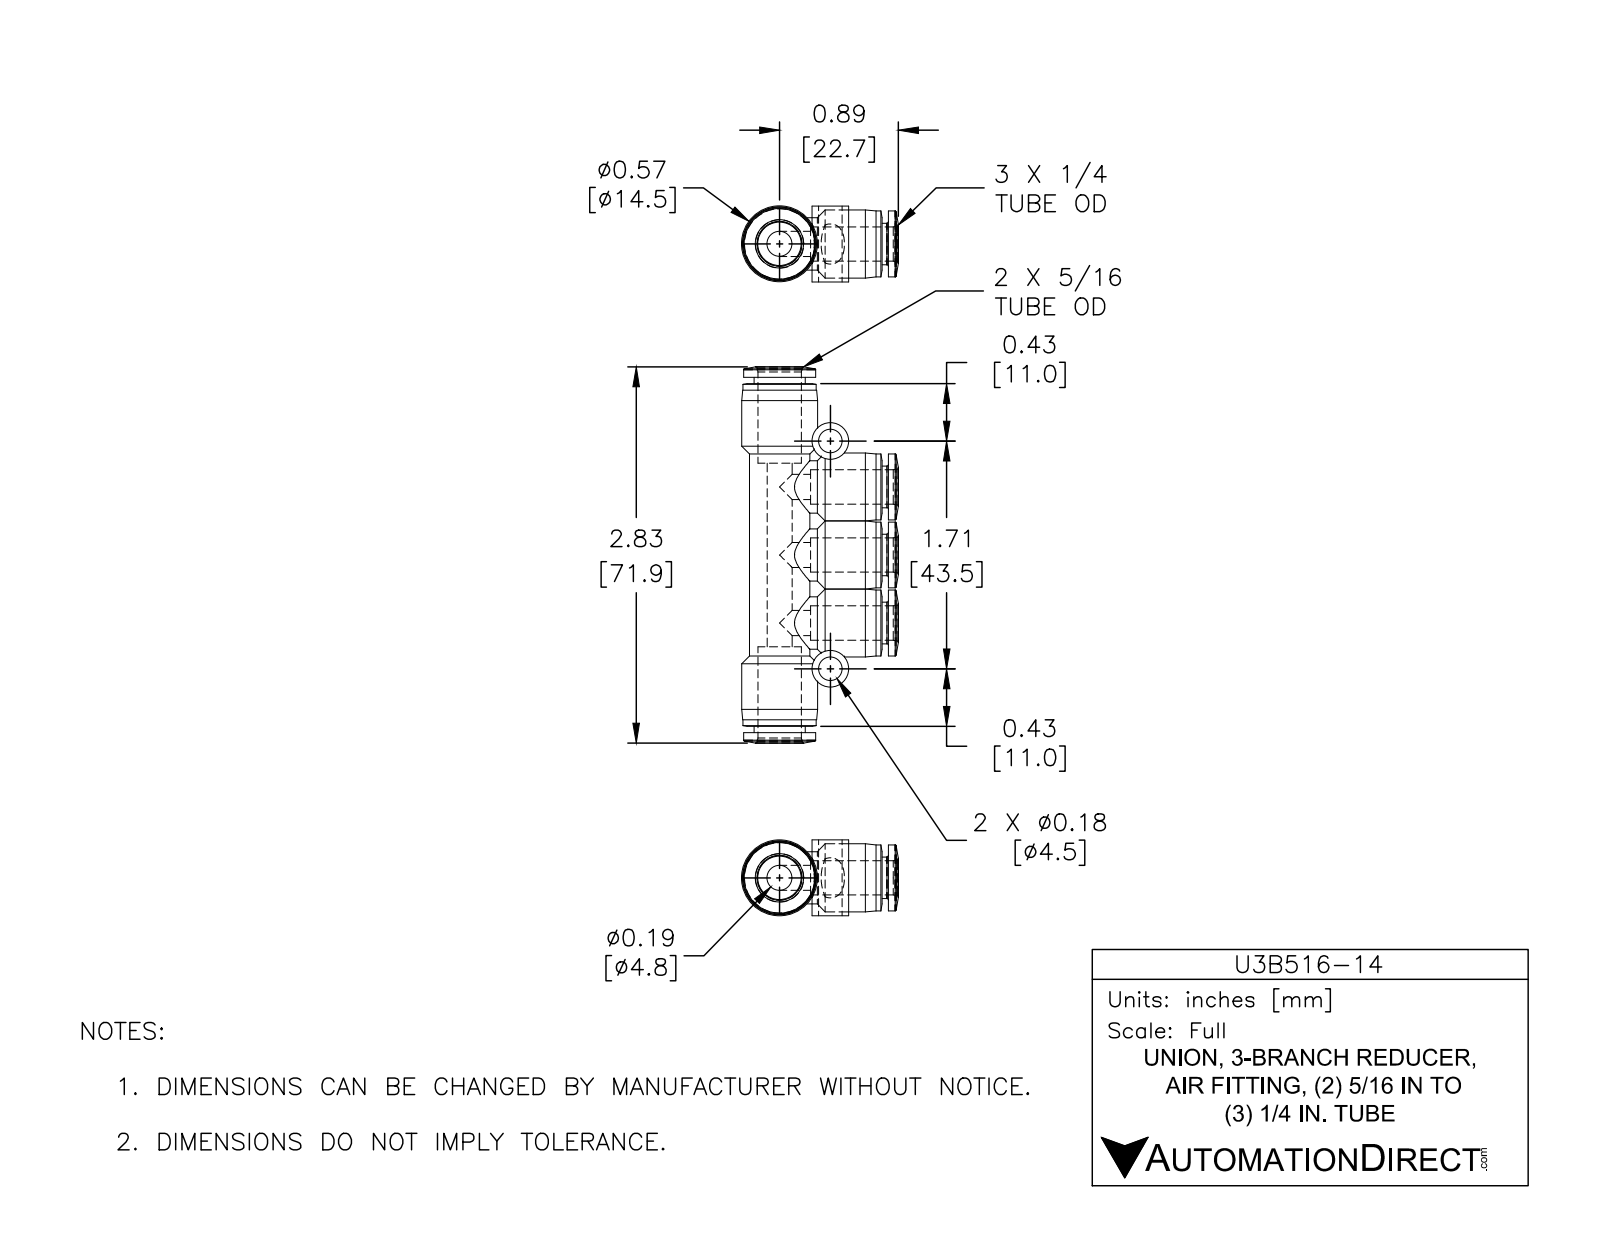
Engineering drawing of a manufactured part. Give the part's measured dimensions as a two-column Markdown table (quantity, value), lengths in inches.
| quantity | value |
| --- | --- |
| part name | U3B516-14 |
| STEP written by | SolidWorks 2015 (CONFIG_CONTROL_DESIGN) |
| units | inches |
| bodies | 1 solid, 174 faces (21 planar, 77 cylindrical, 76 other) |
| overall size | 2.831 × 1.179 × 0.571 |
| volume | 0.68 in³ |
| surface area | 14.73 in² |
| round holes (diameter × count) | 0.189 × 4, 0.258 × 3, 0.177 × 2, 0.327 × 1 |
| round bosses / shafts (diameter × count) | 0.512 × 3, 0.496 × 3, 0.394 × 3, 0.313 × 3, 0.276 × 2, 0.571 × 1, 0.551 × 1, 0.543 × 1 |
| main face-to-face distances | 0.047, 2.626, 2.673, 0.646, 2.028, 0.598, 1.98, 2.579, 0.539, 0.587 |
| hole center spacings | 0.512, 1.024, 1.713 |
